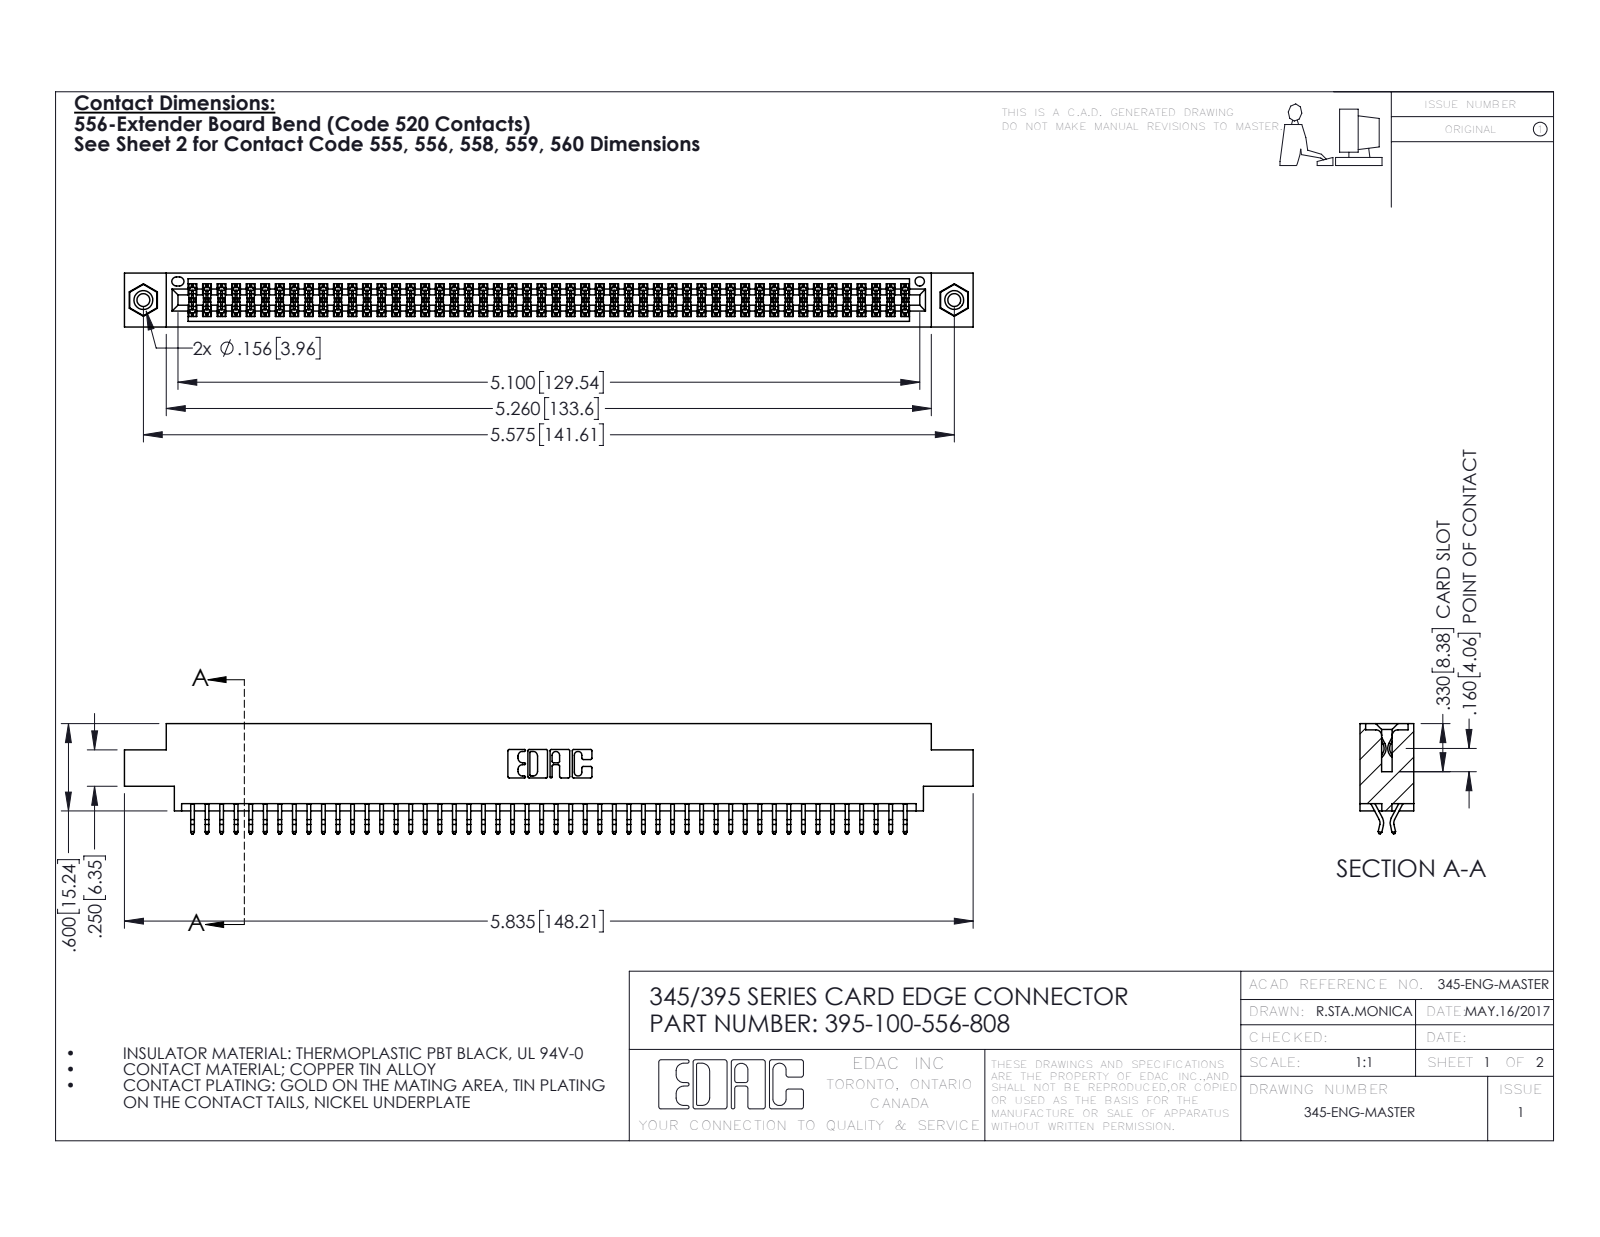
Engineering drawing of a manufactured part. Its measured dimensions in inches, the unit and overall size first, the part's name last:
Units: inches
Overall size (bounding box): 5.835 × 0.757 × 0.37
Round holes (diameter × count): ⌀0.089 ×2, ⌀0.125 ×2, ⌀0.156 ×2, ⌀0.064 ×1
Round bosses / shafts (diameter × count): ⌀0.155 ×2
Partial cylindrical surfaces — rounded edges, fillets, slot ends (radius × count): R0.006 ×150, R0.01 ×22, R0.007 ×6, R0.031 ×6, R0.026 ×3, R0.01 ×2, R0.014 ×2, R0.019 ×2
Main face-to-face distances: 0.072, 0.298, 0.37, 0.2, 0.025, 0.098, 0.272, 0.225, 0.175, 0.149
Hole centre spacings: 0.27, 5.339, 5.575
Volume: 0.876 in³ · Surface area: 33.22 in²
Bodies: 103 solids, 5790 faces (3816 planar, 1958 cylindrical, 16 other)
Part name (STEP PRODUCT): 345 Part_0.170 Offset - 0.156 Dia-TI; 395-100-556-808; 345-292-001_556 Tail; 345-250-001_345-250-003-102
STEP written by: SolidWorks 2016 (CONFIG_CONTROL_DESIGN)
